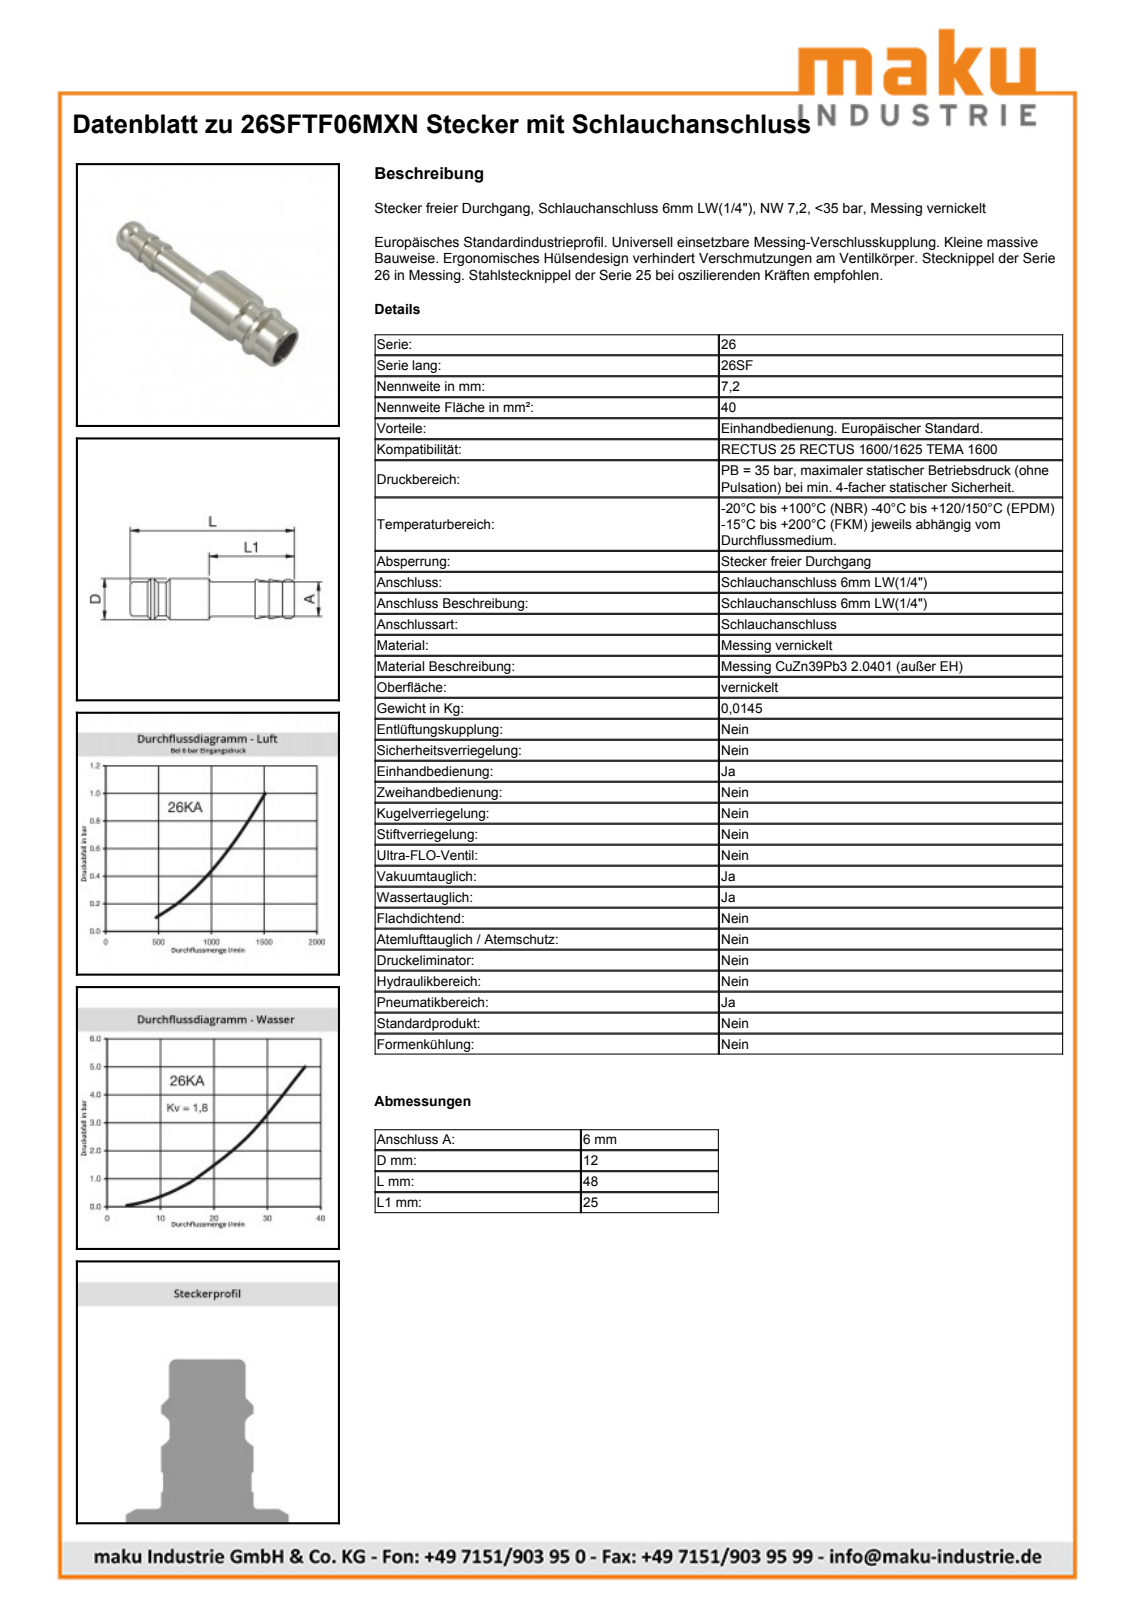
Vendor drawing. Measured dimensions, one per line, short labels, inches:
name: D106787
written by: Autodesk Inventor 2013 (AUTOMOTIVE_DESIGN)
unit: in
bodies: 1 solid, 24 faces (4 planar, 7 cylindrical, 13 other)
size: 1.89 × 0.472 × 0.472
volume: 0.105 in³; area: 3.663 in²
holes: 1× ⌀0.161, 1× ⌀0.309
bosses: 1× ⌀0.472, 1× ⌀0.394, 1× ⌀0.384, 1× ⌀0.24
face distances: 0.984, 0.531, 0.453, 0.906, 1.437, 1.89
